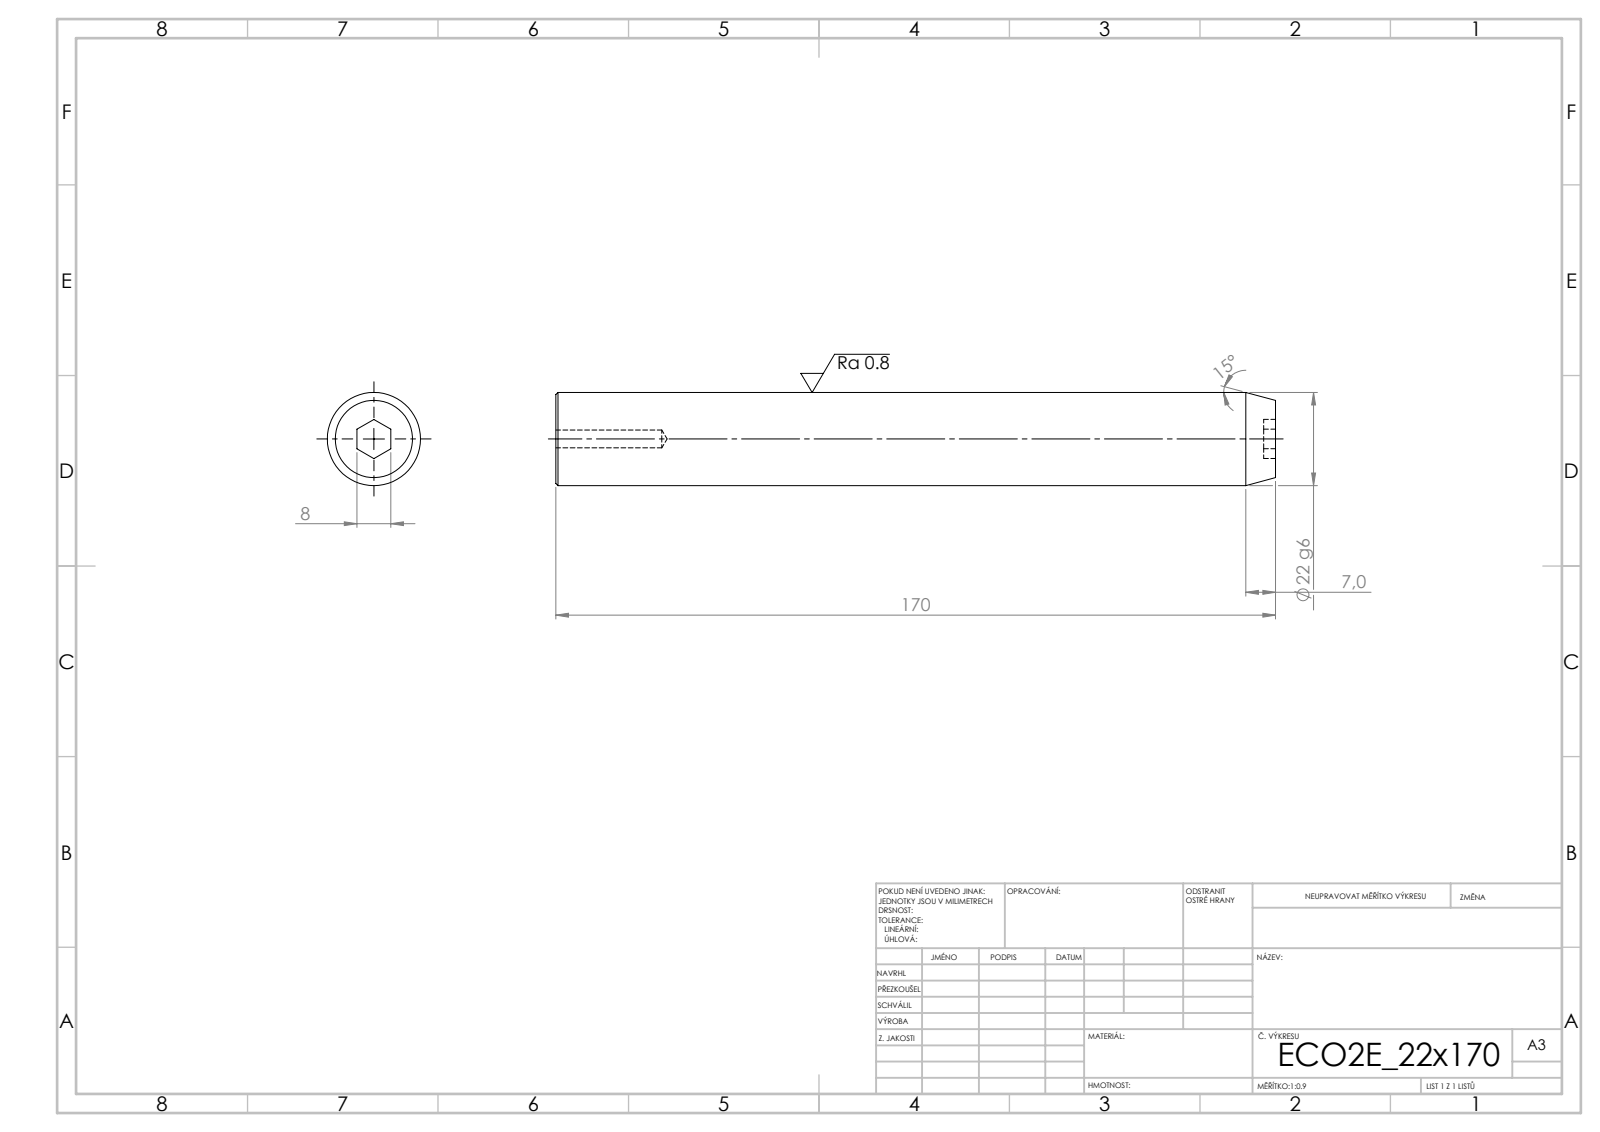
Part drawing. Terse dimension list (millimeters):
written by: SolidWorks 2019 (CONFIG_CONTROL_DESIGN)
unit: mm
bodies: 1 solid, 19 faces (9 planar, 4 cylindrical, 6 other)
size: 170 × 22 × 22
volume: 63 679 mm³; area: 12 755 mm²
holes: 1× ⌀4.2
bosses: 1× ⌀22
face distances: 170, 2.8, 167.2, 8
